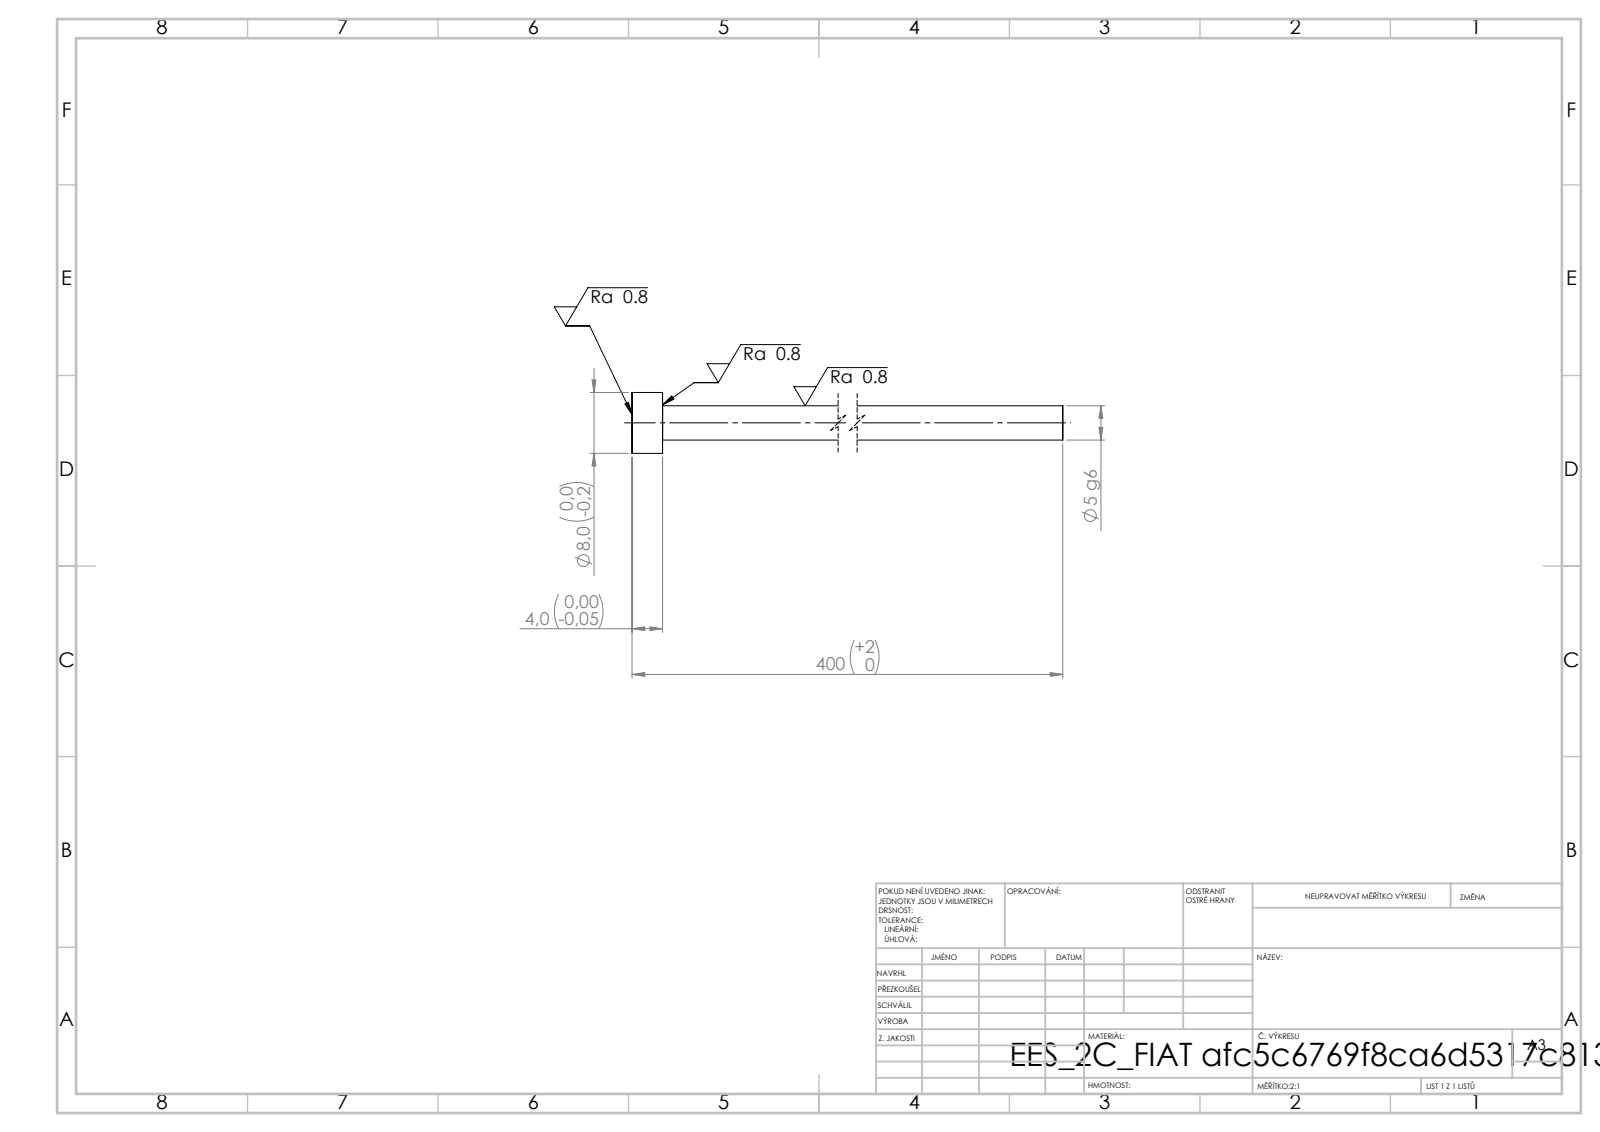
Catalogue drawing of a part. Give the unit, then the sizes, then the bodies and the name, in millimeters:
Units: millimetres
Overall size (bounding box): 400 × 8 × 8
Round bosses / shafts (diameter × count): ⌀8 ×1, ⌀4.5 ×1
Main face-to-face distances: 4, 400, 396
Volume: 6 499 mm³ · Surface area: 5 799 mm²
Bodies: 1 solid, 7 faces (3 planar, 4 cylindrical, 0 other)
STEP written by: SolidWorks 2019 (CONFIG_CONTROL_DESIGN)
